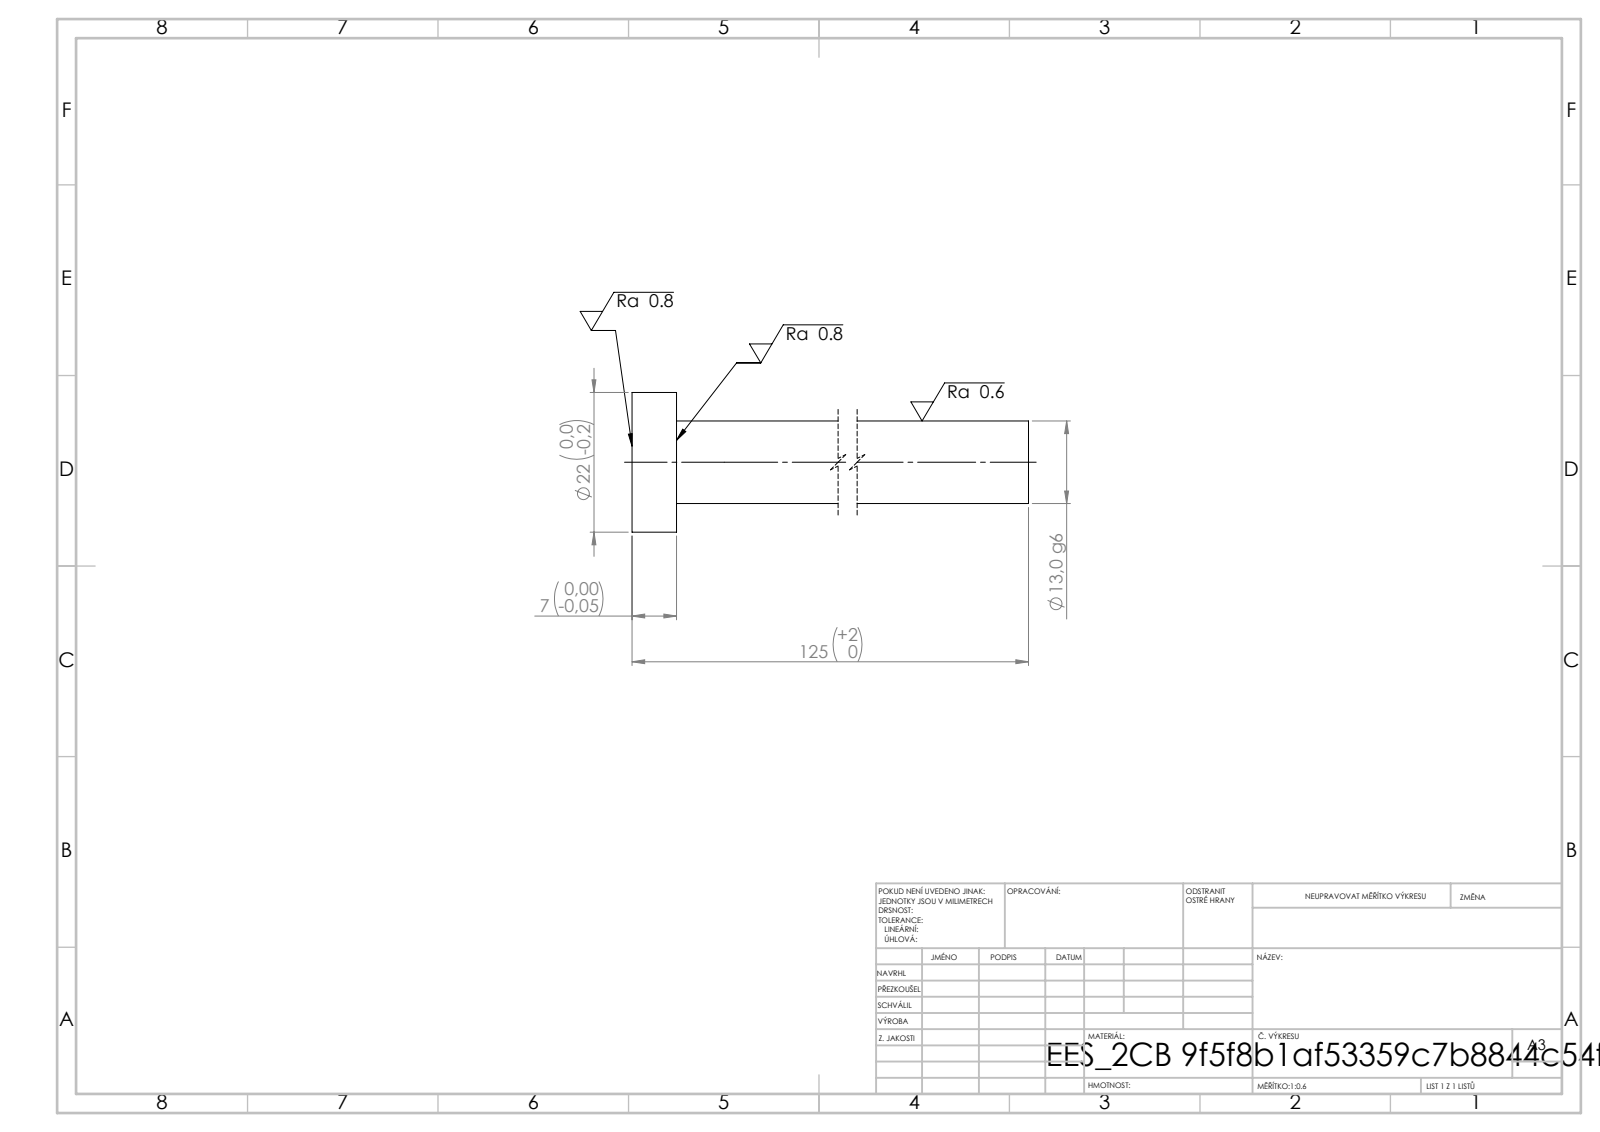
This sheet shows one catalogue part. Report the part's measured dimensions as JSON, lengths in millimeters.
{"step_written_by": "SolidWorks 2019 (CONFIG_CONTROL_DESIGN)", "units": "millimeters", "bodies": {"solids": 1, "faces": 7, "planar": 3, "cylindrical": 4, "other": 0}, "overall_size": [125, 22, 22], "volume_mm3": 18323, "surface_area_mm2": 6063, "round_bosses_or_shafts": [[22, 1], [13, 1]], "face_to_face_distances": [7, 125, 118]}
